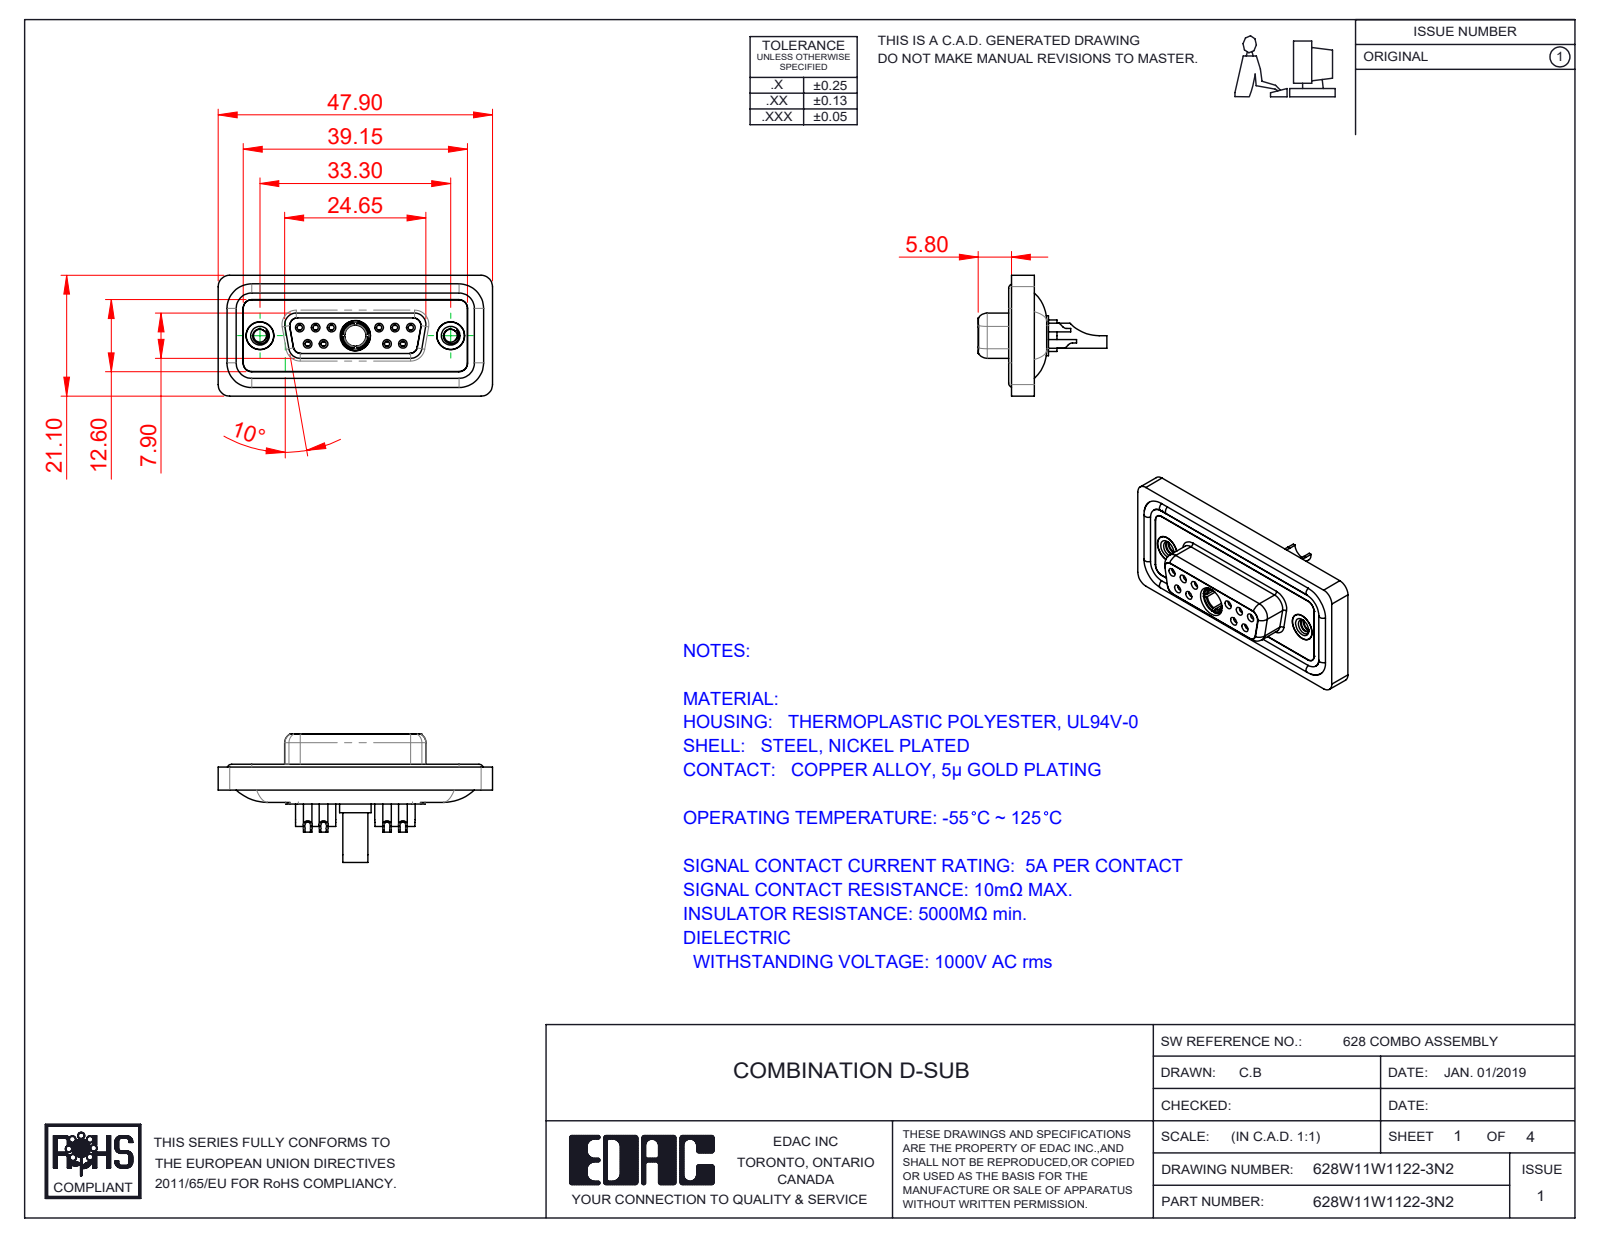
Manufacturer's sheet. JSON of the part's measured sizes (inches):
{"part_name": "628W11W1122-3N2; Power Socket_30A SC; 628Combo Contact Row 2_22; 628Combo Threaded Rivet_2 (+5 more)", "step_written_by": "SolidWorks 2020 (CONFIG_CONTROL_DESIGN)", "units": "inches", "bodies": {"solids": 19, "faces": 1016, "planar": 307, "cylindrical": 424, "other": 285}, "overall_size": [1.886, 0.884, 0.831], "volume_in3": 0.376, "surface_area_in2": 15.87, "round_holes": [[0.035, 10], [0.039, 10], [0.043, 10], [0.059, 10], [0.079, 10], [0.067, 6], [0.063, 4], [0.191, 3], [0.089, 2], [0.157, 2], [0.159, 2], [0.197, 2]], "round_bosses_or_shafts": [[0.087, 10], [0.063, 10], [0.195, 2], [0.189, 2], [0.217, 1], [0.205, 1], [0.195, 1], [0.187, 1]], "partial_cylinders_radius": [[0.059, 22], [0.079, 20], [0.053, 12], [0.063, 8], [0.039, 6], [0.01, 4], [0.02, 4], [0.024, 4]], "face_to_face_distances": [0.016, 0.063, 0.071, 0.114, 0.02, 0.043, 0.222, 0.293, 0.26, 0.278], "hole_center_spacings": [0.124, 0.109, 0.545, 0.436, 0.654, 0.198, 0.198, 0.218]}
